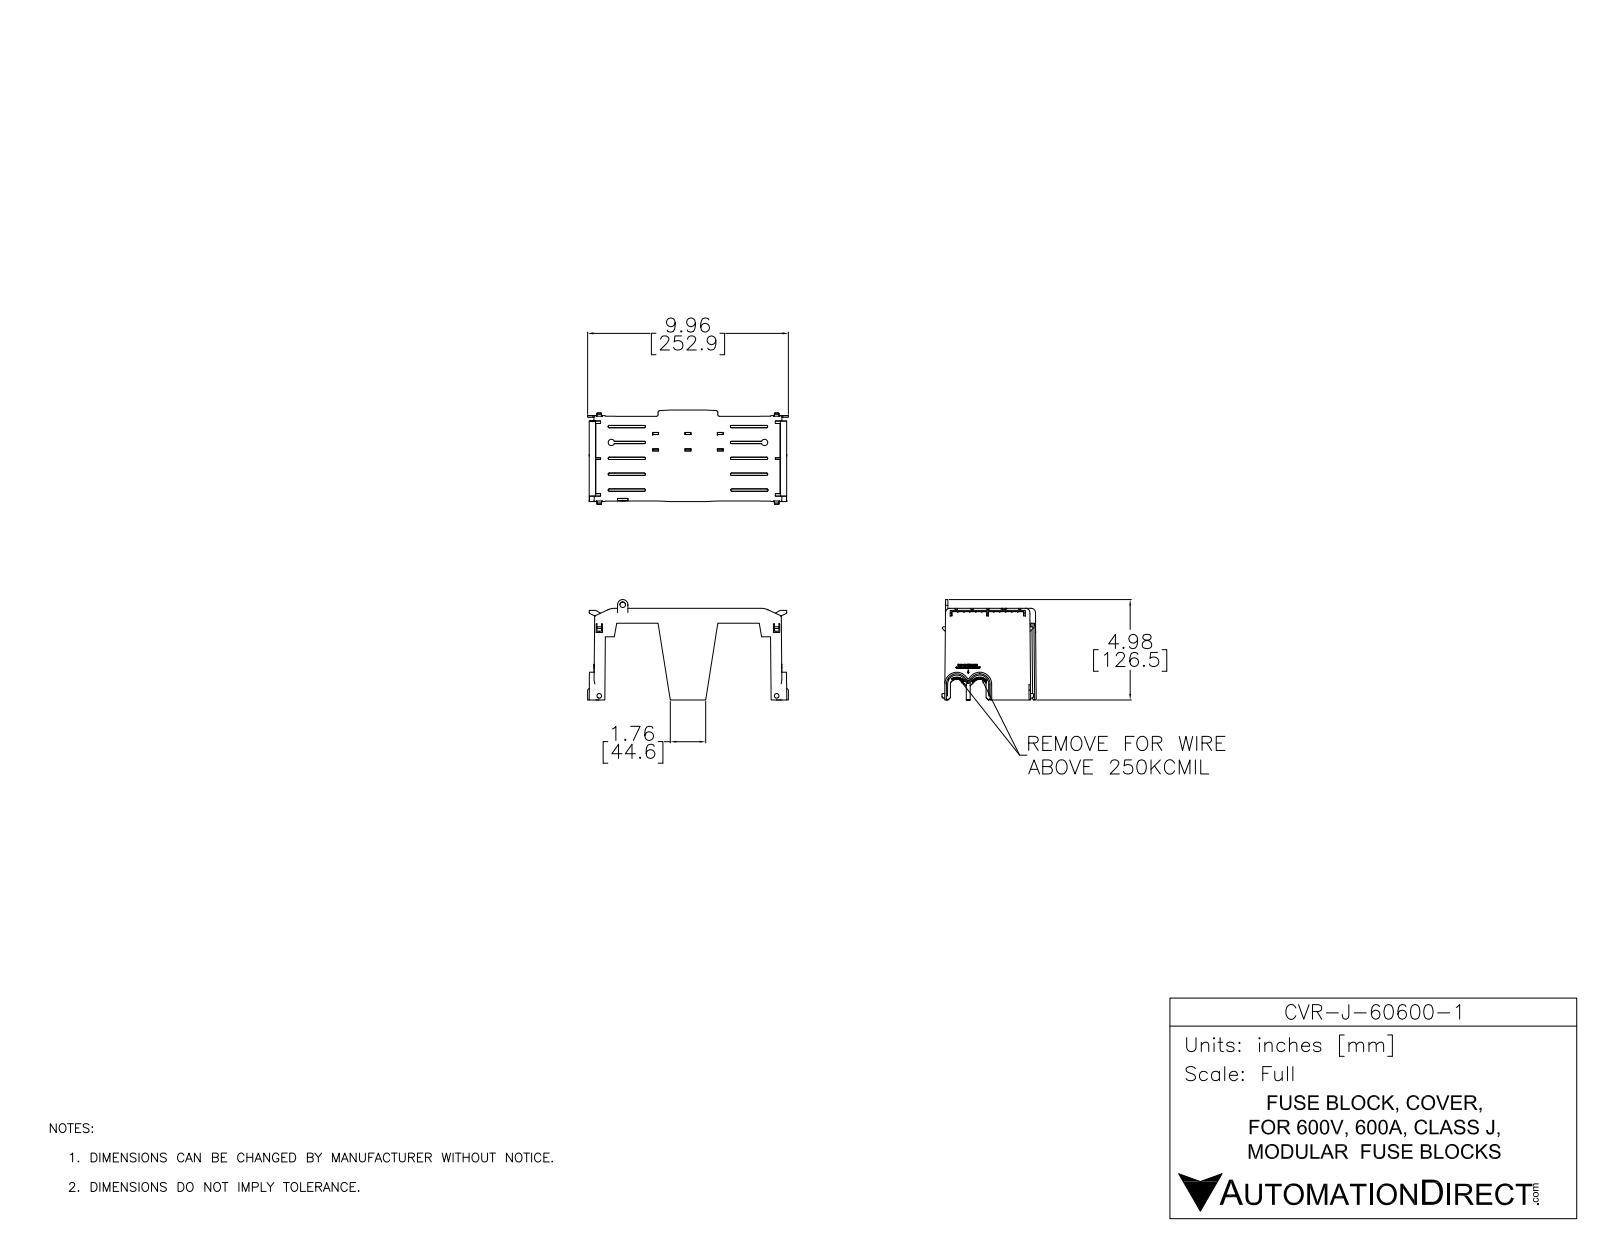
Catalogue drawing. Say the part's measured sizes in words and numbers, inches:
The part is named "CVR-J-60600-1". Its 3-D file was written by "SolidWorks 2017 (AUTOMOTIVE_DESIGN)". It is 1 solid with 2344 faces: 1597 planar, 167 cylindrical and 580 other. Overall it measures 9.959 by 4.983 by 4.677 inches. Its volume is 10.27 cubic inches and its surface area 271.3 square inches. Round holes: 1 of diameter 0.276. Partial cylindrical surfaces (rounded edges, fillets, slot ends): 18 of radius 0.039, 12 of radius 0.118, 10 of radius 0.028, 9 of radius 0.217, 7 of radius 0.138, 6 of radius 0.079, 4 of radius 0.354, 4 of radius 0.512. The main face-to-face distances are 0.079, 0.079, 0.276, 0.197, 0.354, 0.803, 0.795, 0.118, 1.614, 0.158.
